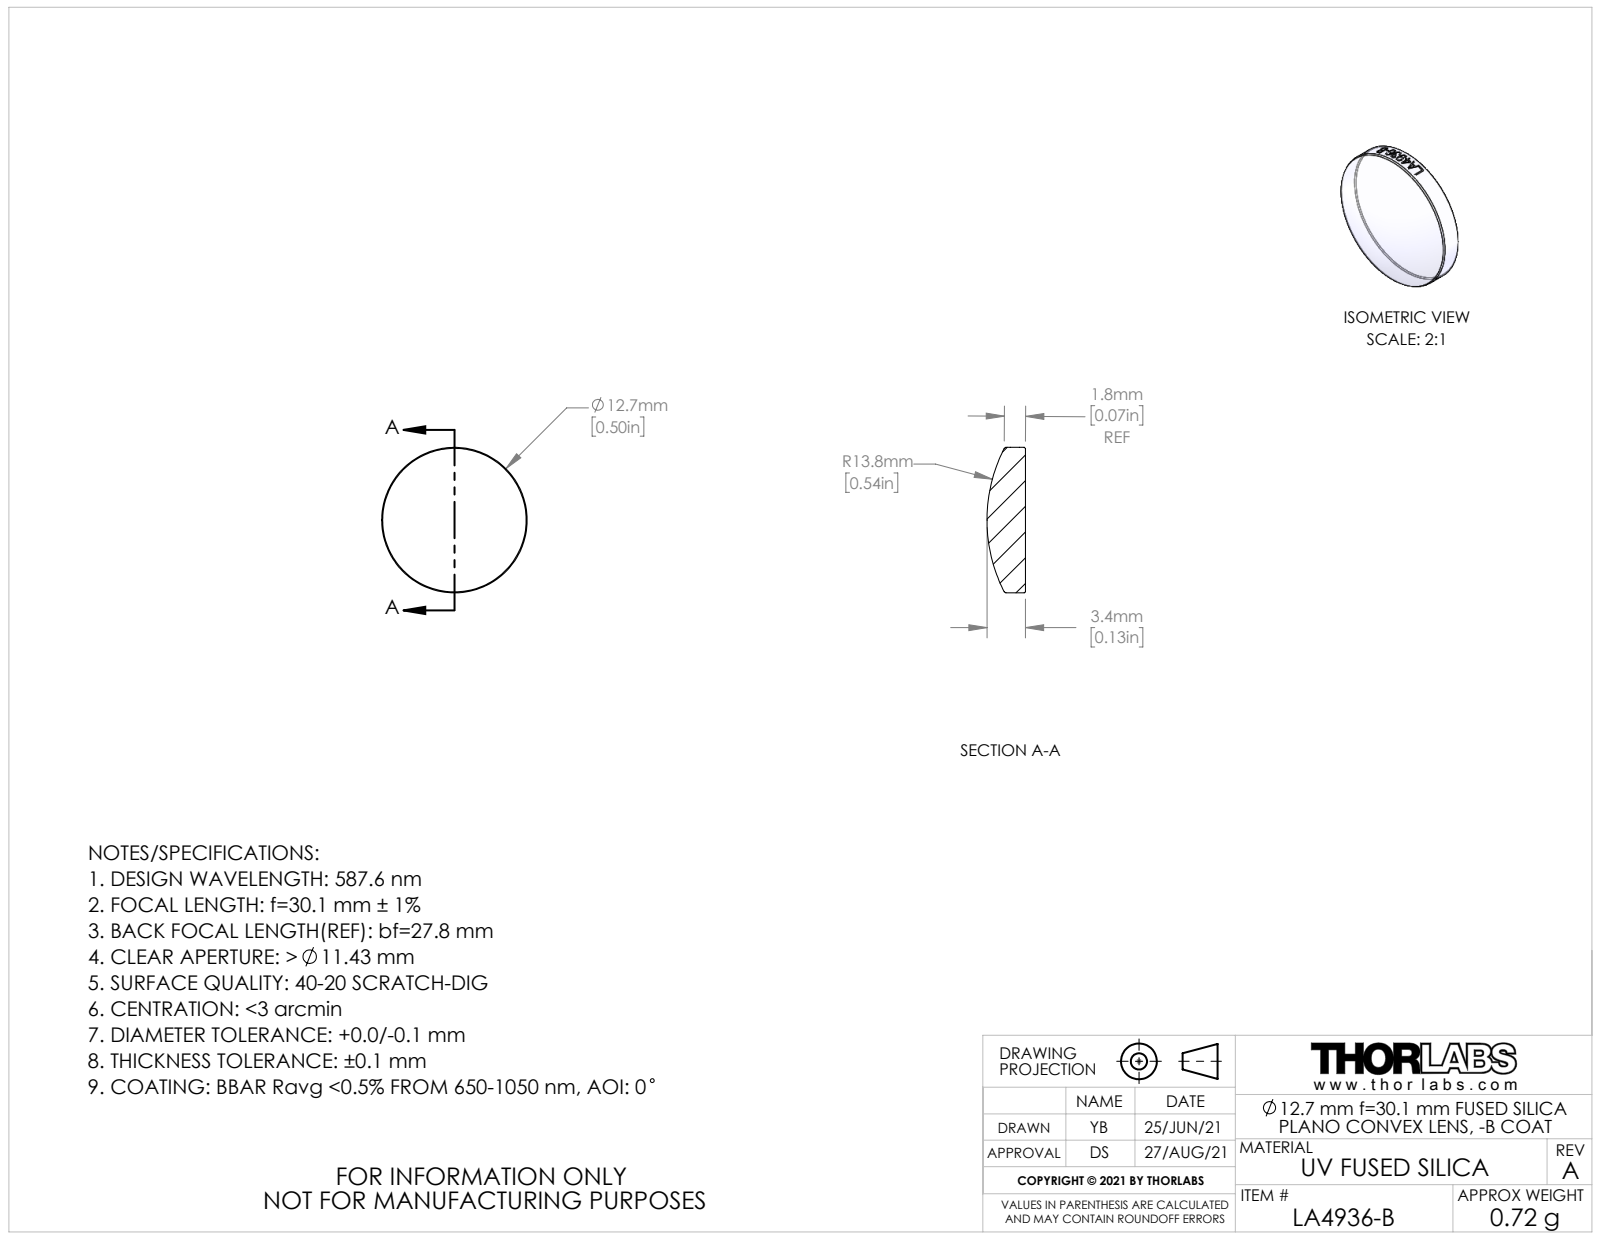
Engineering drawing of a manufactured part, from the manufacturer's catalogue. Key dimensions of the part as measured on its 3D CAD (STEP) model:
Part name (STEP PRODUCT): CTN017894-E0W
STEP written by: SolidWorks 2018 (AUTOMOTIVE_DESIGN)
Units: millimetres
Bodies: 1 solid, 23 faces (1 planar, 16 cylindrical, 6 other)
Overall size (bounding box): 12.7 × 12.7 × 3.35
Volume: 328 mm³ · Surface area: 329 mm²
Round bosses / shafts (diameter × count): ⌀12.7 ×1
